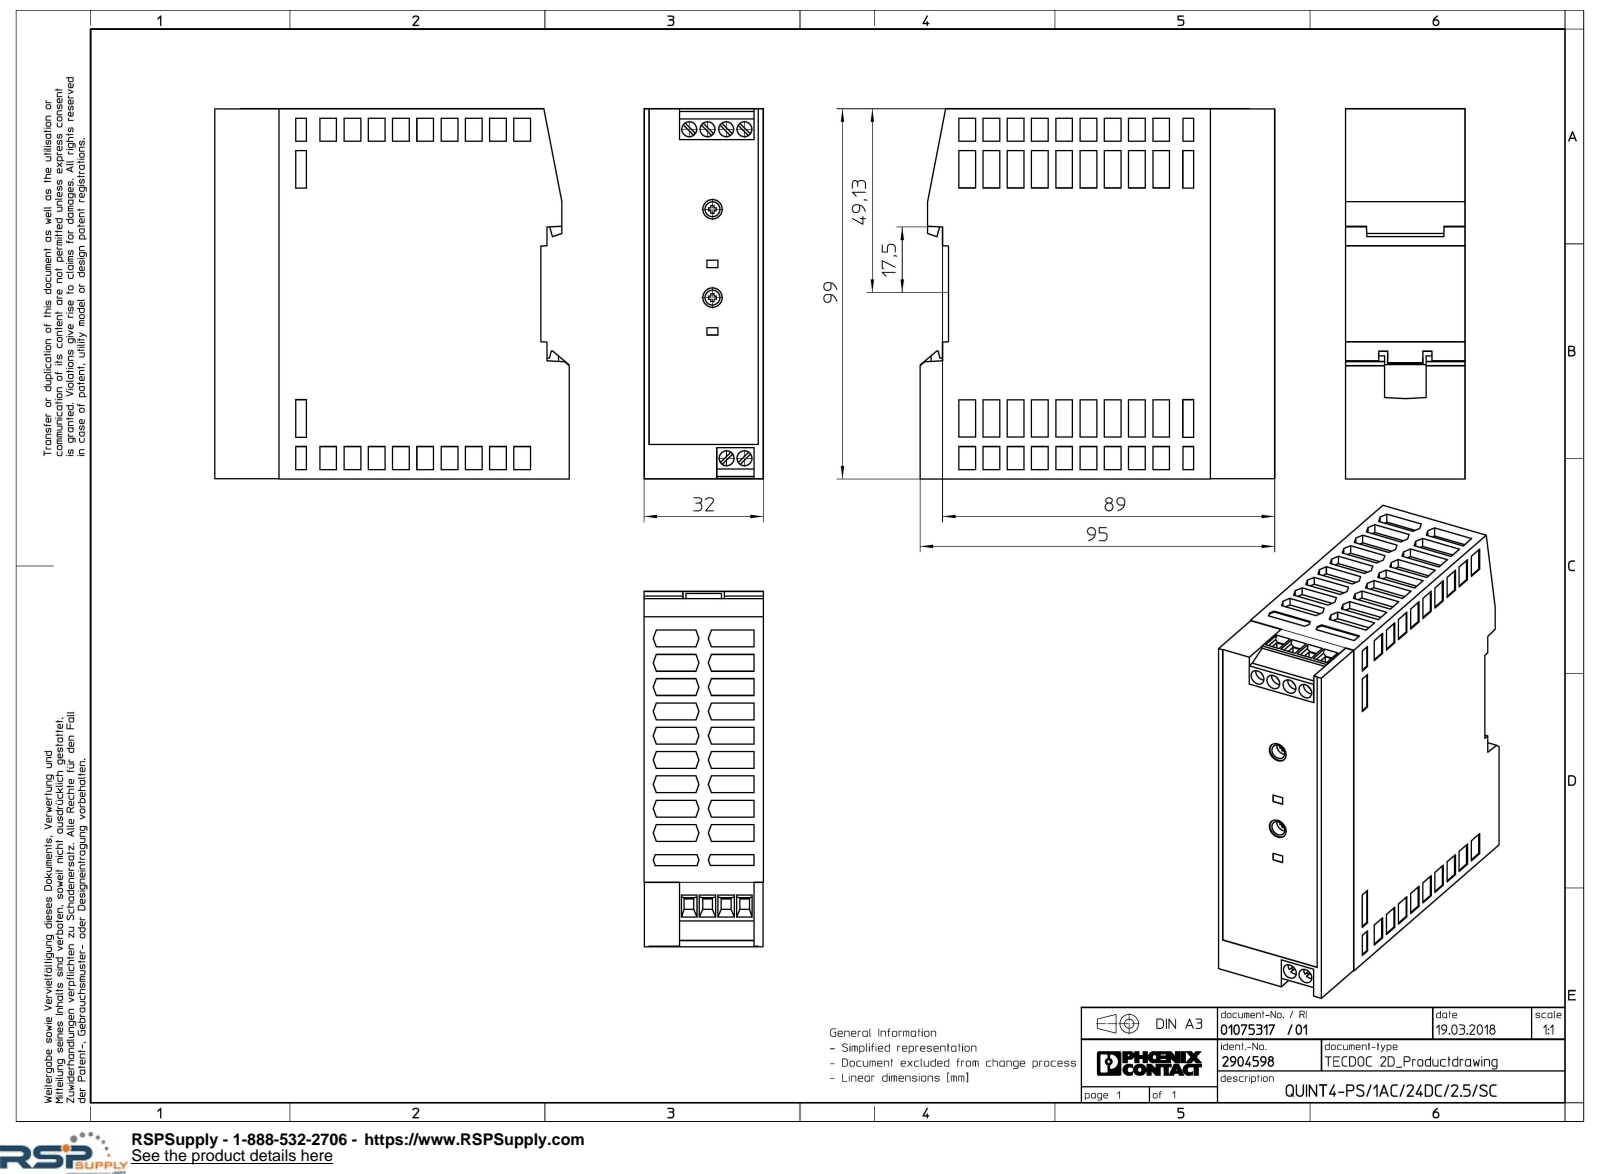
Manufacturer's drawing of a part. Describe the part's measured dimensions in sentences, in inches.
The part is named "QUINT4_PS_1AC_24DC_2.5_SC-select". Its 3-D file was written by "Creo Elements/Direct Modeling 20.1A 29-Sep-2018 (C) Parametric Technology GmbH (AUTOMOTIVE_DESIGN)". It is 1 solid with 830 faces: 810 planar, 20 cylindrical and 0 other. Overall it measures 3.898 by 3.74 by 1.26 inches. Its volume is 17.23 cubic inches and its surface area 53.42 square inches. Round holes: 8 of diameter 0.157, 2 of diameter 0.205. The main face-to-face distances are 1.26, 1.256, 1.249, 1.245, 1.252, 3.898, 0.256, 3.736, 0.512, 0.079. The hole center spacings are 0.193, 0.39, 3.462, 0.189, 0.197, 0.583, 0.844, 0.854.
